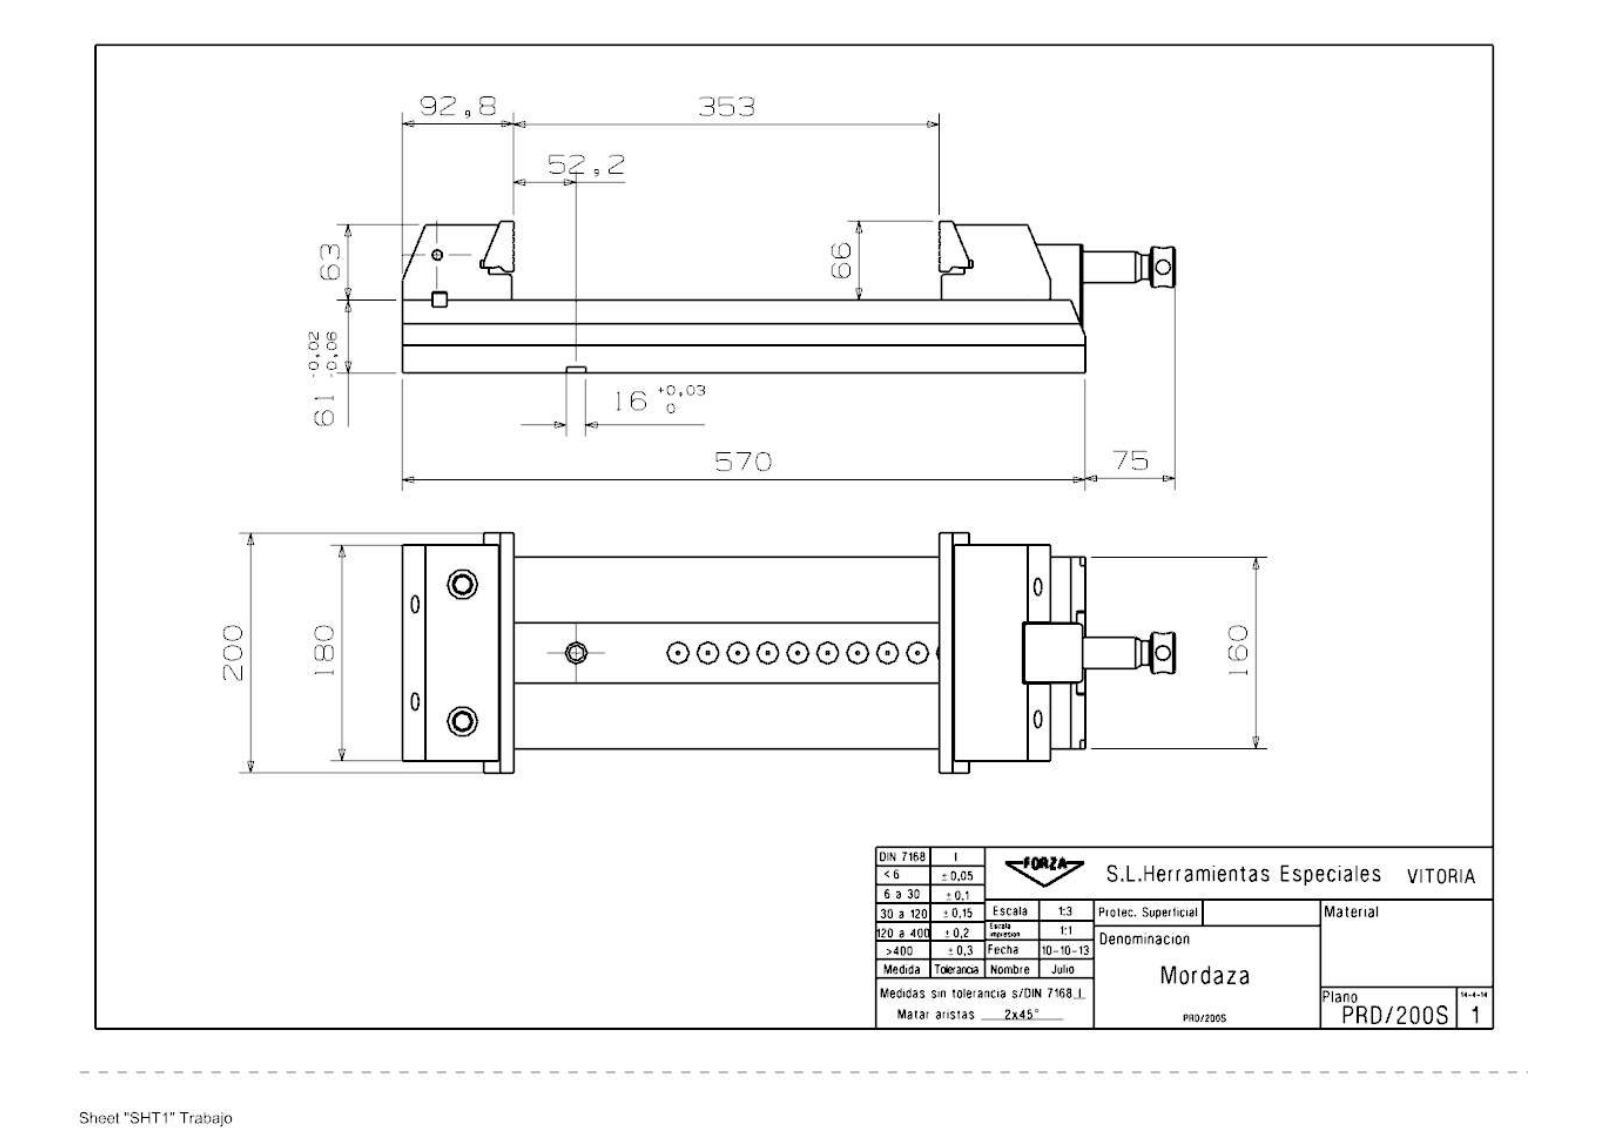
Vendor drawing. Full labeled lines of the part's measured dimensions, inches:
Part name (STEP PRODUCT): 30150070 Montaje Taco Hus; PRD_200S_Mordaza
STEP written by: SIEMENS PLM Software NX 9.0 (CONFIG_CONTROL_DESIGN)
Units: inches
Bodies: 11 solids, 465 faces (269 planar, 130 cylindrical, 66 other)
Overall size (bounding box): 25.394 × 7.874 × 4.998
Volume: 382.1 in³ · Surface area: 1 007 in²
Round holes (diameter × count): ⌀0.591 ×6, ⌀0.204 ×5, ⌀0.512 ×5, ⌀0.275 ×4, ⌀0.335 ×4, ⌀0.394 ×4, ⌀0.346 ×3, ⌀0.417 ×3, ⌀0.748 ×3, ⌀0.472 ×2, ⌀0.487 ×2, ⌀0.566 ×2
Round bosses / shafts (diameter × count): ⌀1.339 ×1, ⌀1.331 ×1, ⌀1.024 ×1, ⌀0.787 ×1, ⌀0.65 ×1
Partial cylindrical surfaces — rounded edges, fillets, slot ends (radius × count): R0.016 ×24, R0.059 ×4, R0.315 ×4, R0.787 ×4, R0.063 ×2, R0.236 ×2, R0.276 ×2, R0.157 ×1
Main face-to-face distances: 2.402, 1.15, 1.252, 2.343, 0.295, 0.059, 6.299, 2.48, 1.091, 4.882
Hole centre spacings: 0.571, 3.76, 3.189, 4.331, 2.677, 0.648, 0.652, 0.948
